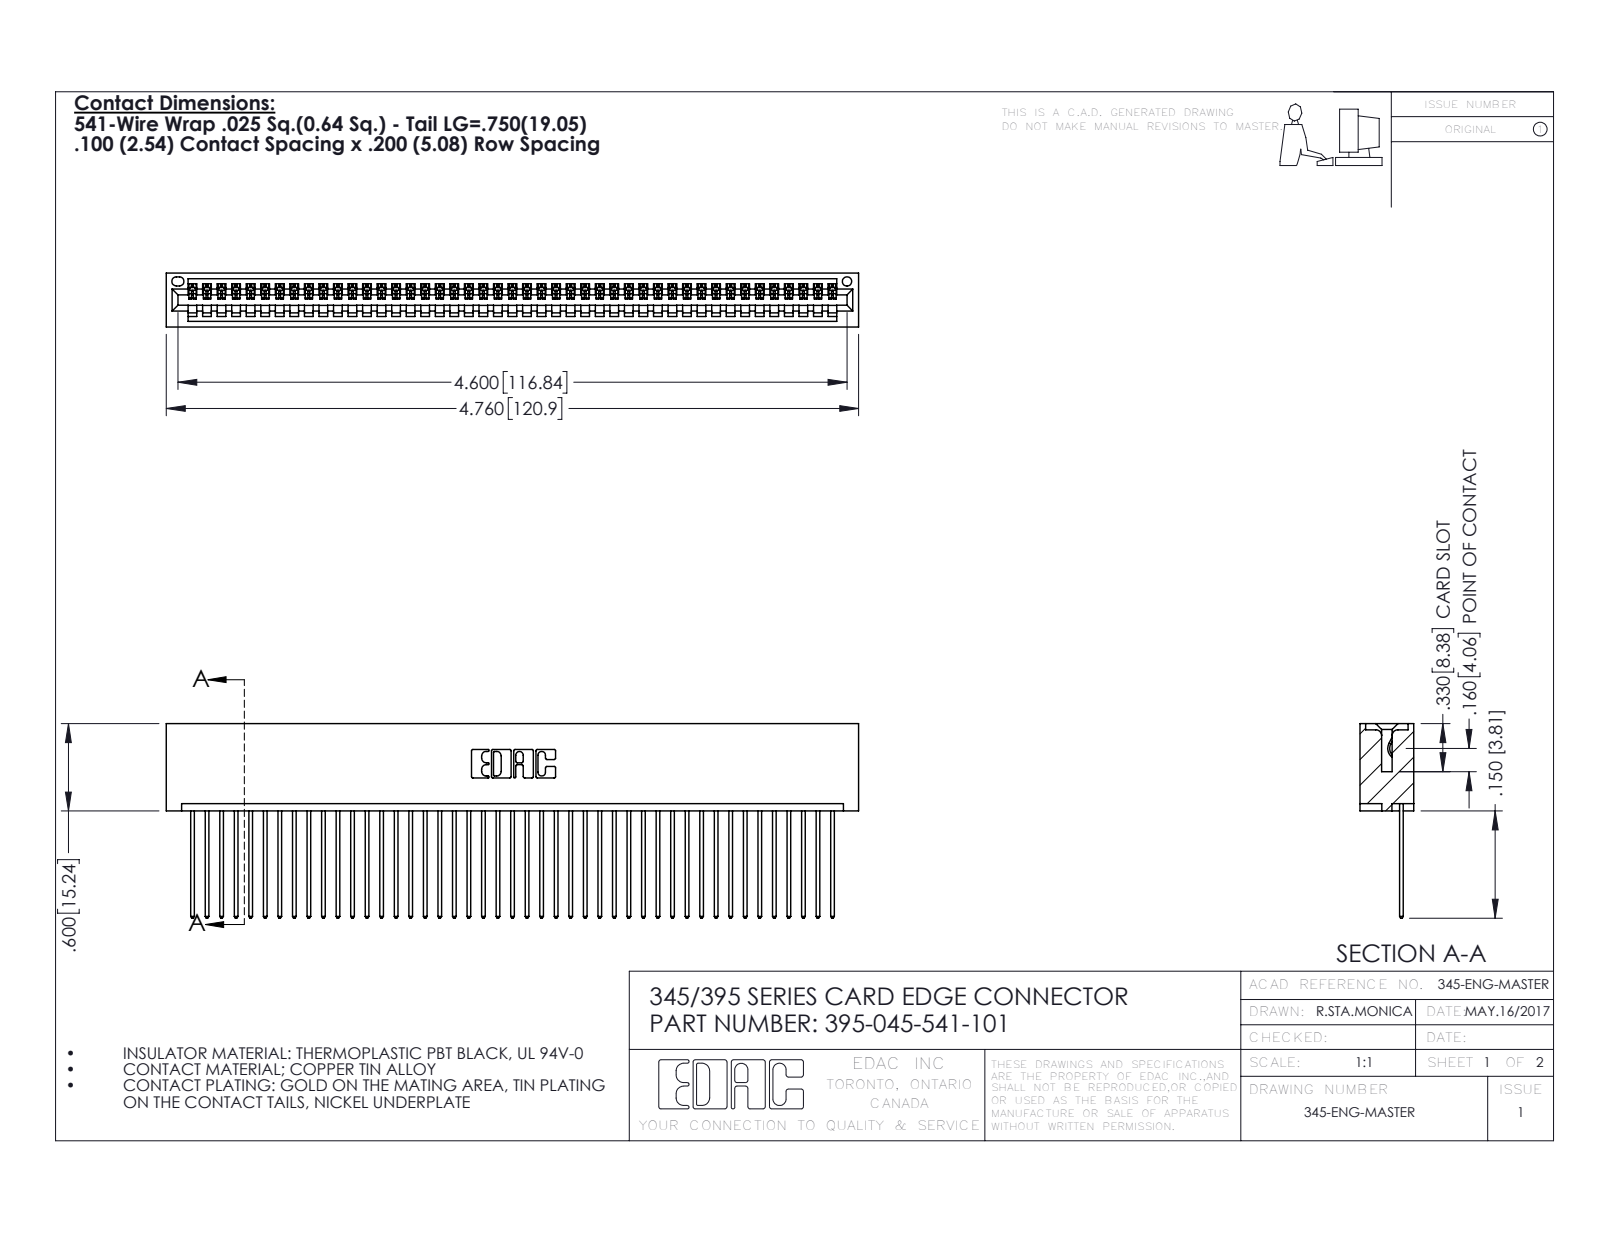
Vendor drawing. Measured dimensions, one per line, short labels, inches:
name: 345 Part_No Mounting Lugs; 395-045-541-101; 345-292-001_345-293-141
written by: SolidWorks 2016 (CONFIG_CONTROL_DESIGN)
unit: in
bodies: 46 solids, 2728 faces (1876 planar, 852 cylindrical, 0 other)
size: 4.76 × 1.337 × 0.37
volume: 0.747 in³; area: 26.93 in²
holes: 1× ⌀0.064
rounds: 90× R0.006, 90× R0.01, 22× R0.01, 6× R0.007, 6× R0.031, 3× R0.026, 2× R0.031, 2× R0.04
face distances: 0.072, 0.298, 0.098, 0.272, 0.025, 0.37, 0.2, 0.225, 0.149, 0.072
